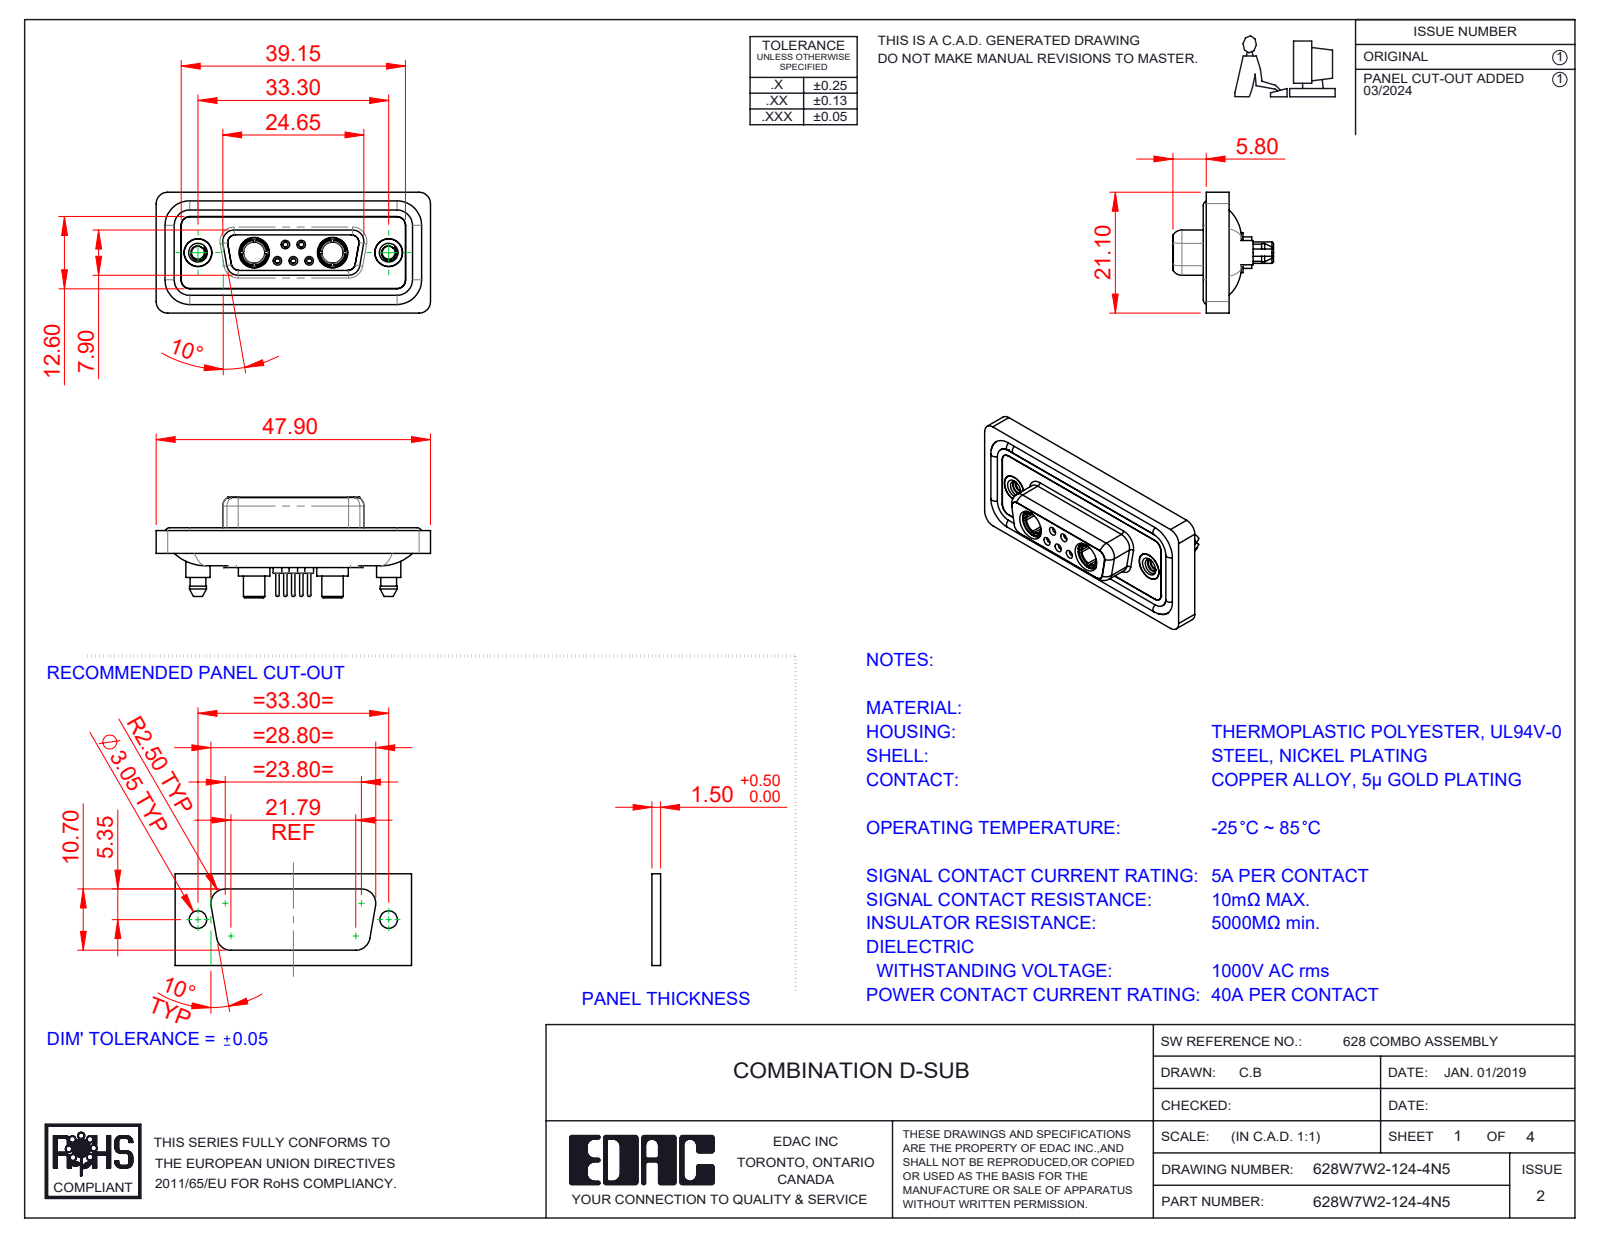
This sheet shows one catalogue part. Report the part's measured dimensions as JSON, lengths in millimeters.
{"part_name": "Power Socket_40A S; 628Combo Contact Row 2_24; 628Combo Waterproof Housing_15 Contacts; 628Combo Contact Row 1_24 (+5 more)", "step_written_by": "SolidWorks 2023 (CONFIG_CONTROL_DESIGN)", "units": "millimeters", "bodies": {"solids": 16, "faces": 859, "planar": 254, "cylindrical": 361, "other": 244}, "overall_size": [47.9, 21.1, 17.55], "volume_mm3": 6248, "surface_area_mm2": 10240, "round_holes": [[0.9, 5], [1.1, 5], [1.5, 5], [2, 5], [4.85, 4], [1.6, 3], [1.7, 2], [2.26, 2], [3.7, 2], [4, 2], [4.05, 2], [5, 2]], "round_bosses_or_shafts": [[1.6, 6], [2.2, 5], [0.6, 5], [5.5, 2], [5.4, 2], [5.2, 2], [4.96, 2], [4.95, 2]], "partial_cylinders_radius": [[1.5, 24], [2, 20], [1.35, 12], [1.6, 10], [0.25, 4], [0.5, 4], [0.6, 4], [0.65, 4]], "face_to_face_distances": [0.4, 1.8, 1.6, 0.5, 2.9, 1.1, 7.45, 5.65, 6.6, 7.05], "hole_center_spacings": [3.16, 2.77, 9.8, 23.5, 4.31, 4.33, 5.03, 5.04]}
